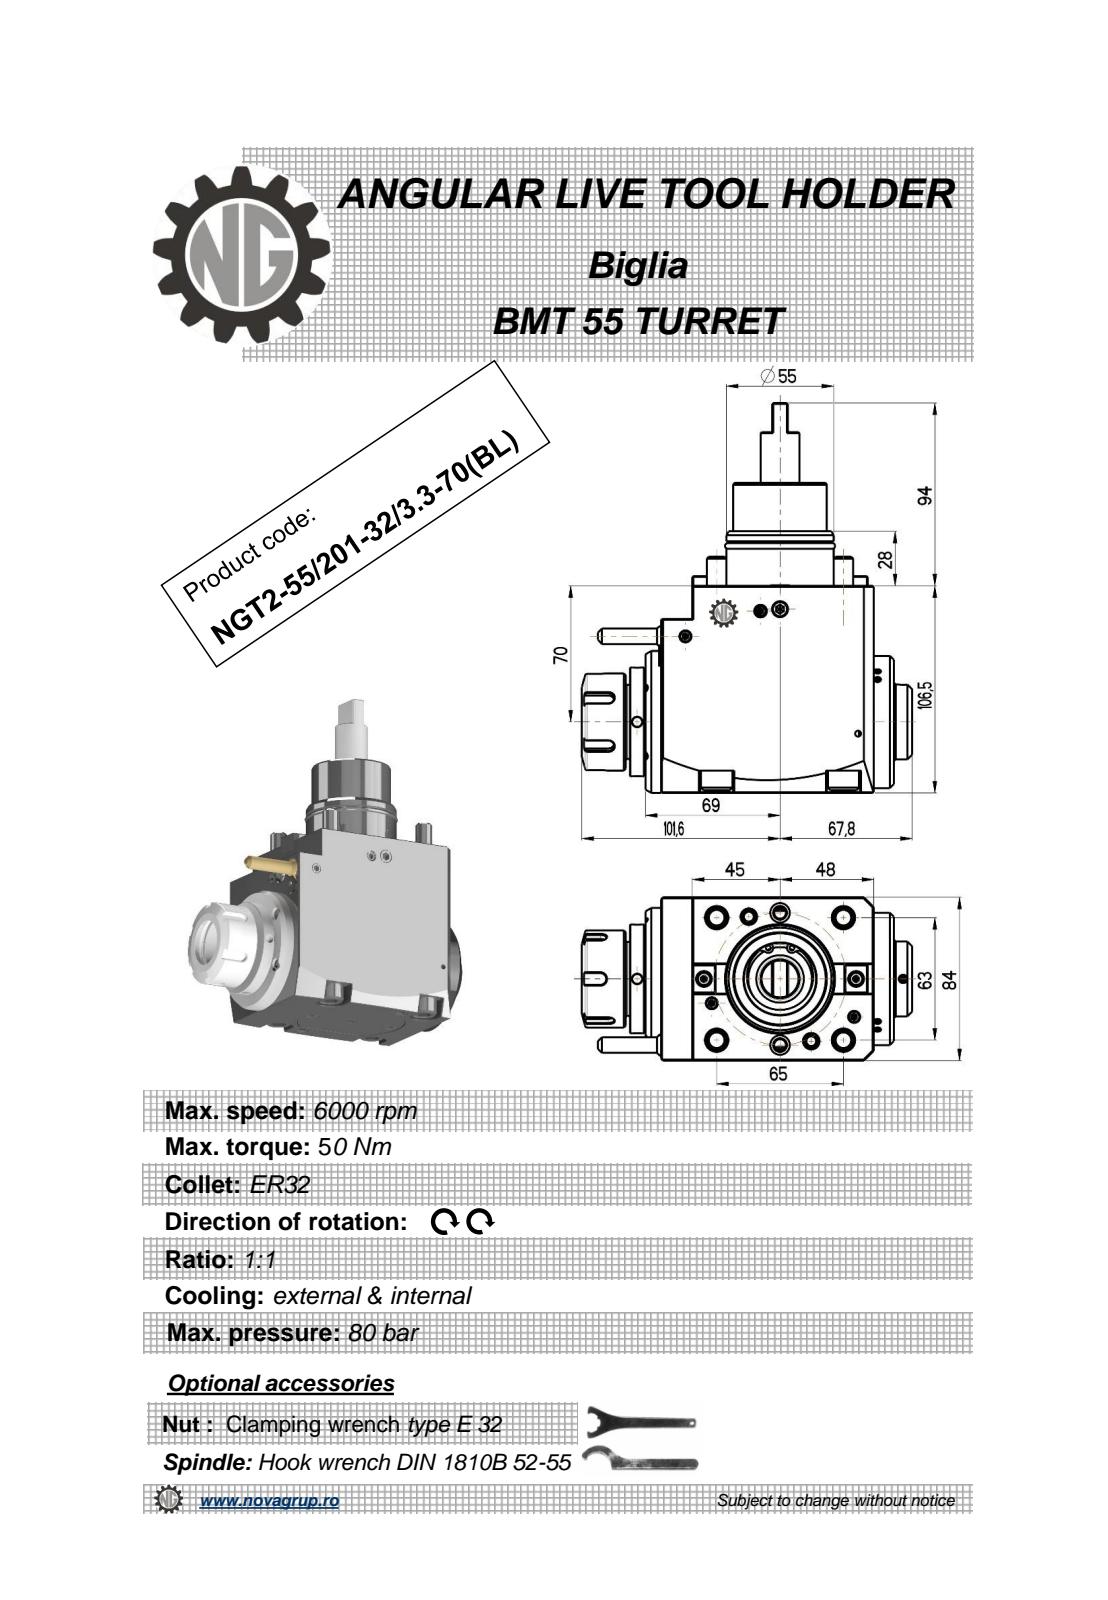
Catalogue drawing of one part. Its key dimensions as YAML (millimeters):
part_name: "NGT2_55_201_25_3_3_70_BL"
step_written_by: "PRO/ENGINEER BY PARAMETRIC TECHNOLOGY CORPORATION, 2010280 (CONFIG_CONTROL_DESIGN)"
units: millimeters
bodies: {solids: 2, faces: 451, planar: 205, cylindrical: 116, other: 130}
overall_size: [200.5, 169.4, 84]
volume: 1210000
surface_area: 92369
round_holes:
  - {diameter: 5, count: 3}
  - {diameter: 6, count: 2}
  - {diameter: 3, count: 1}
  - {diameter: 27, count: 1}
round_bosses_or_shafts:
  - {diameter: 16, count: 4}
  - {diameter: 10, count: 4}
  - {diameter: 50, count: 2}
  - {diameter: 73, count: 1}
  - {diameter: 68, count: 1}
  - {diameter: 56, count: 1}
  - {diameter: 55, count: 1}
  - {diameter: 48, count: 1}
partial_cylinders:
  - {radius: 0.32, count: 20}
  - {radius: 0.22, count: 6}
  - {radius: 3, count: 5}
  - {radius: 8.5, count: 4}
  - {radius: 0.8, count: 2}
  - {radius: 480, count: 2}
  - {radius: 3.4, count: 1}
  - {radius: 4, count: 1}
face_to_face_distances: [84, 106.5, 8, 109, 16, 117, 127.3, 119.3, 10.3, 17]
hole_center_spacings: [80.76, 55.61, 68]
